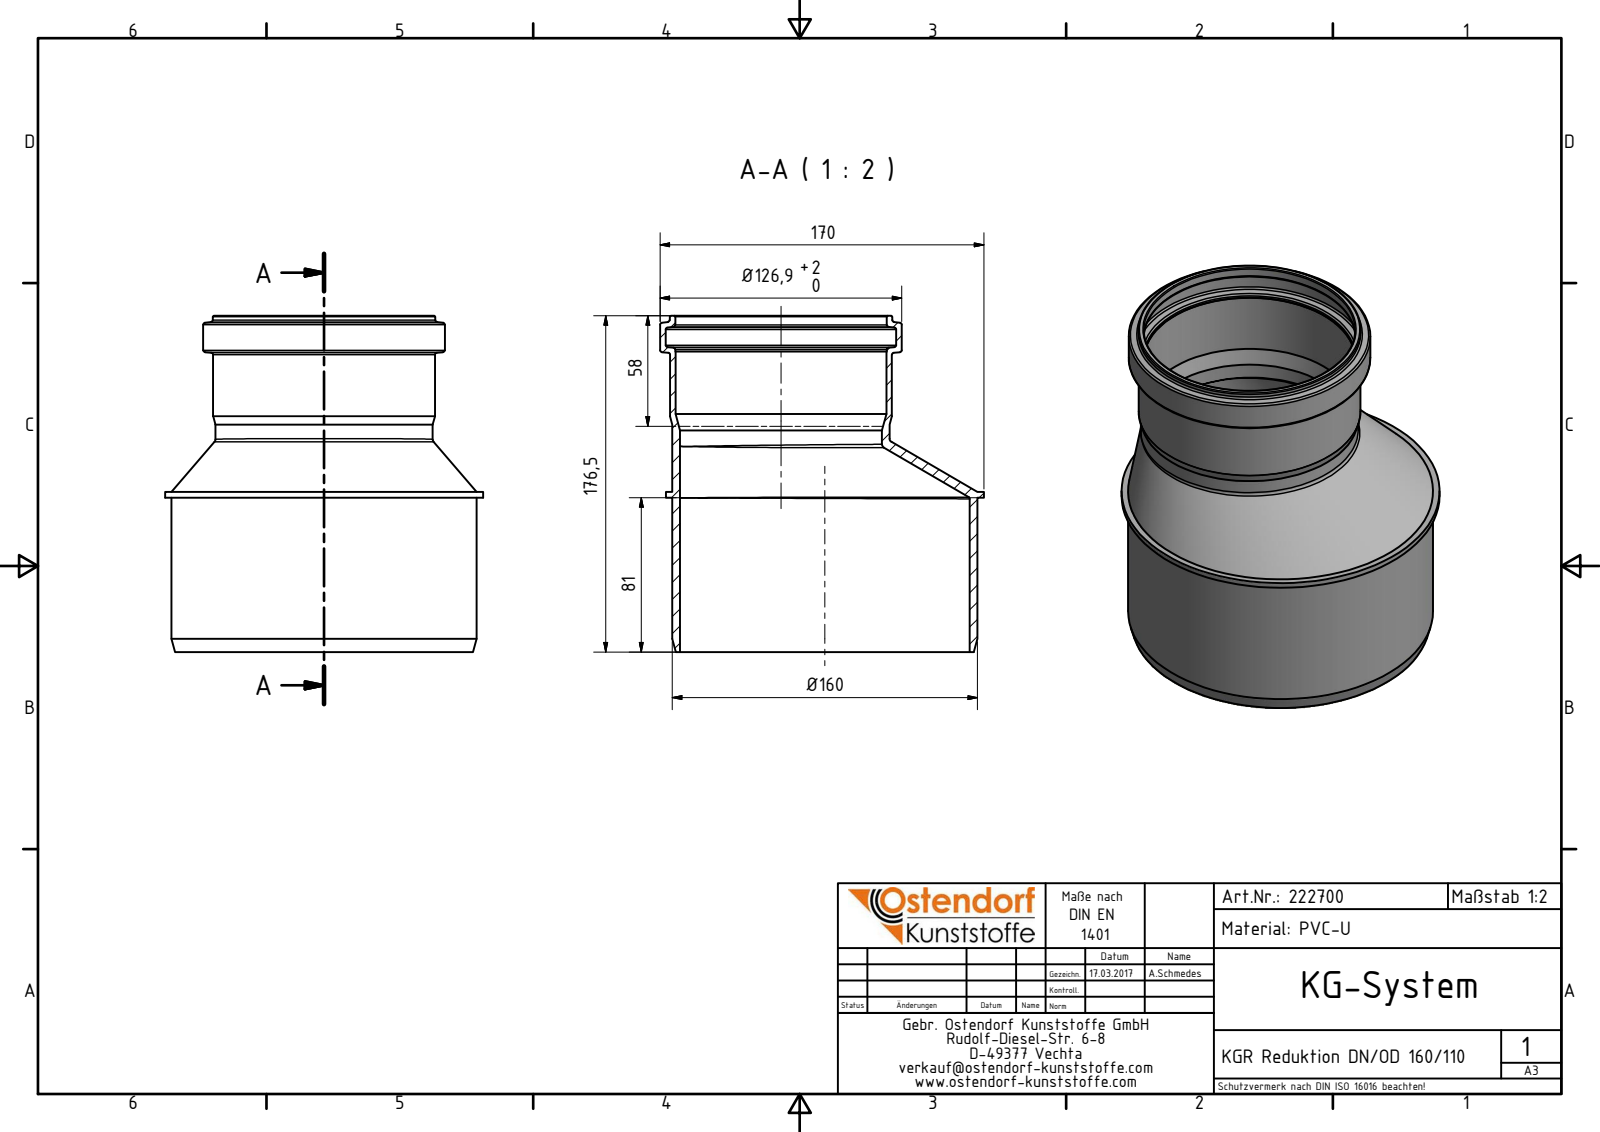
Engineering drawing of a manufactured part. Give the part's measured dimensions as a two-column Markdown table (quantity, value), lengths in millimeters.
| quantity | value |
| --- | --- |
| part name | 222700 KGR Reduktion DN_OD 160_110 |
| STEP written by | Autodesk Inventor 2016 (AUTOMOTIVE_DESIGN) |
| units | millimeters |
| bodies | 1 solid, 40 faces (5 planar, 12 cylindrical, 23 other) |
| overall size | 176.5 × 170 × 167 |
| volume | 321 915 mm³ |
| surface area | 172 591 mm² |
| round holes (diameter × count) | 106.1 × 1, 110.7 × 1, 111 × 1, 121.1 × 1, 152.2 × 1 |
| round bosses / shafts (diameter × count) | 167 × 1, 160.2 × 1, 126.9 × 1, 116.8 × 1, 116.5 × 1, 114.1 × 1 |
| main face-to-face distances | 3, 81, 84, 176.5, 95.5, 92.5, 157.67, 76.67, 73.67, 18.83 |
| hole center spacings | 23.05 |
